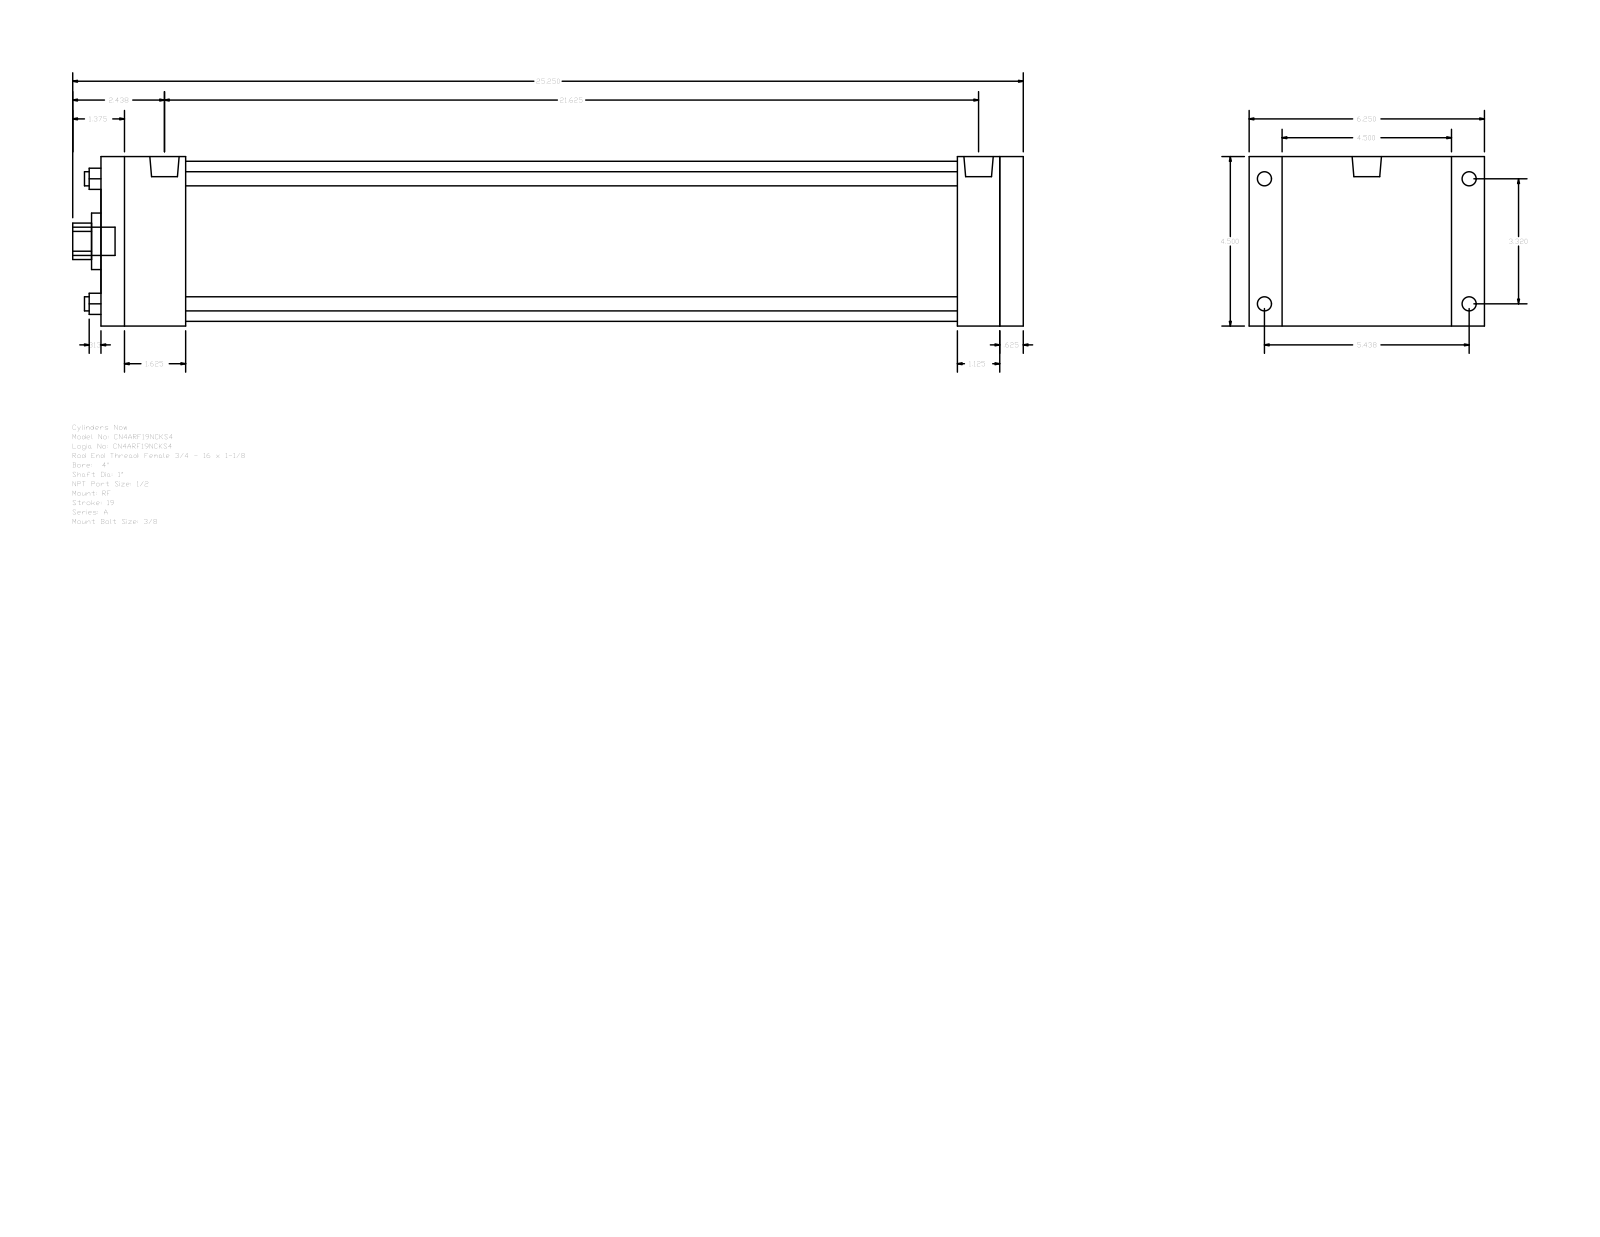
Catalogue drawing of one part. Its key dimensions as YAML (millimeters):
part_name: "A_RF__0400_1"
step_written_by: "GSSL Pune (CONFIG_CONTROL_DESIGN)"
units: millimeters
bodies: {solids: 0, faces: 92, planar: 64, cylindrical: 28, other: 0}
overall_size: [641.35, 158.75, 114.3]
round_holes:
  - {diameter: 9.53, count: 4}
  - {diameter: 25.4, count: 1}
  - {diameter: 38.1, count: 1}
  - {diameter: 107.95, count: 1}
round_bosses_or_shafts:
  - {diameter: 9.53, count: 4}
  - {diameter: 8.73, count: 4}
  - {diameter: 19.77, count: 2}
  - {diameter: 19.05, count: 1}
partial_cylinders:
  - {radius: 12.29, count: 1}
face_to_face_distances: [114.3, 622.3, 15.87, 606.43, 22.23, 136.53, 577.85, 28.58, 44.45, 57.15]
hole_center_spacings: [59.62, 84.32, 119.25]
